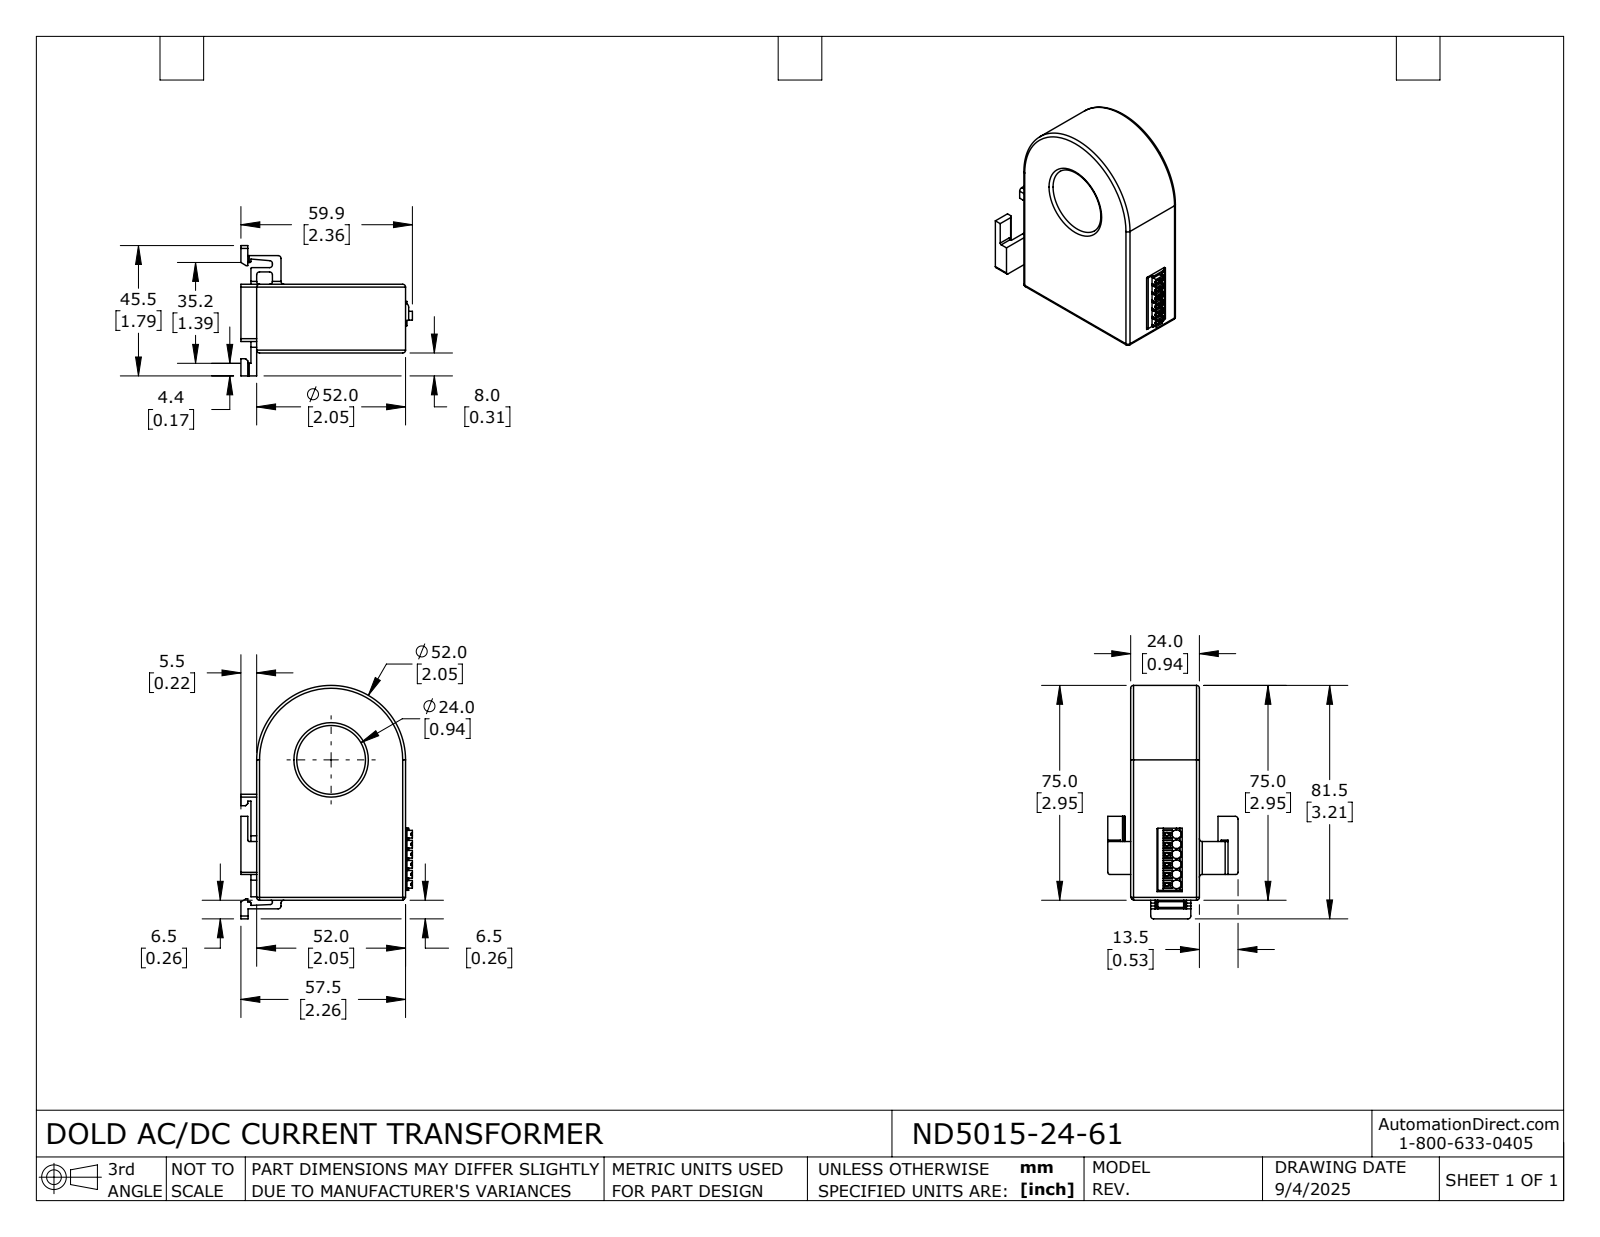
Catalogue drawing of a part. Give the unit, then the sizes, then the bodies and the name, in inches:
Units: inches
Overall size (bounding box): 3.209 × 2.358 × 1.791
Round holes (diameter × count): ⌀0.047 ×6, ⌀0.945 ×1
Partial cylindrical surfaces — rounded edges, fillets, slot ends (radius × count): R0.039 ×26, R0.02 ×12, R0.071 ×8, R0.01 ×4, R0.071 ×4, R0.014 ×2, R0.03 ×2, R0.079 ×2
Main face-to-face distances: 0.945, 2.126, 0.079, 2.047, 0.138, 0.217, 2.264, 0.118, 0.094, 0.157
Hole centre spacings: 0.138, 0.276, 0.413, 0.551, 0.689
Volume: 4.851 in³ · Surface area: 26.99 in²
Bodies: 1 solid, 407 faces (288 planar, 97 cylindrical, 22 other)
Part name (STEP PRODUCT): ND5015-024-61
STEP written by: SolidWorks 2024 (AUTOMOTIVE_DESIGN)
